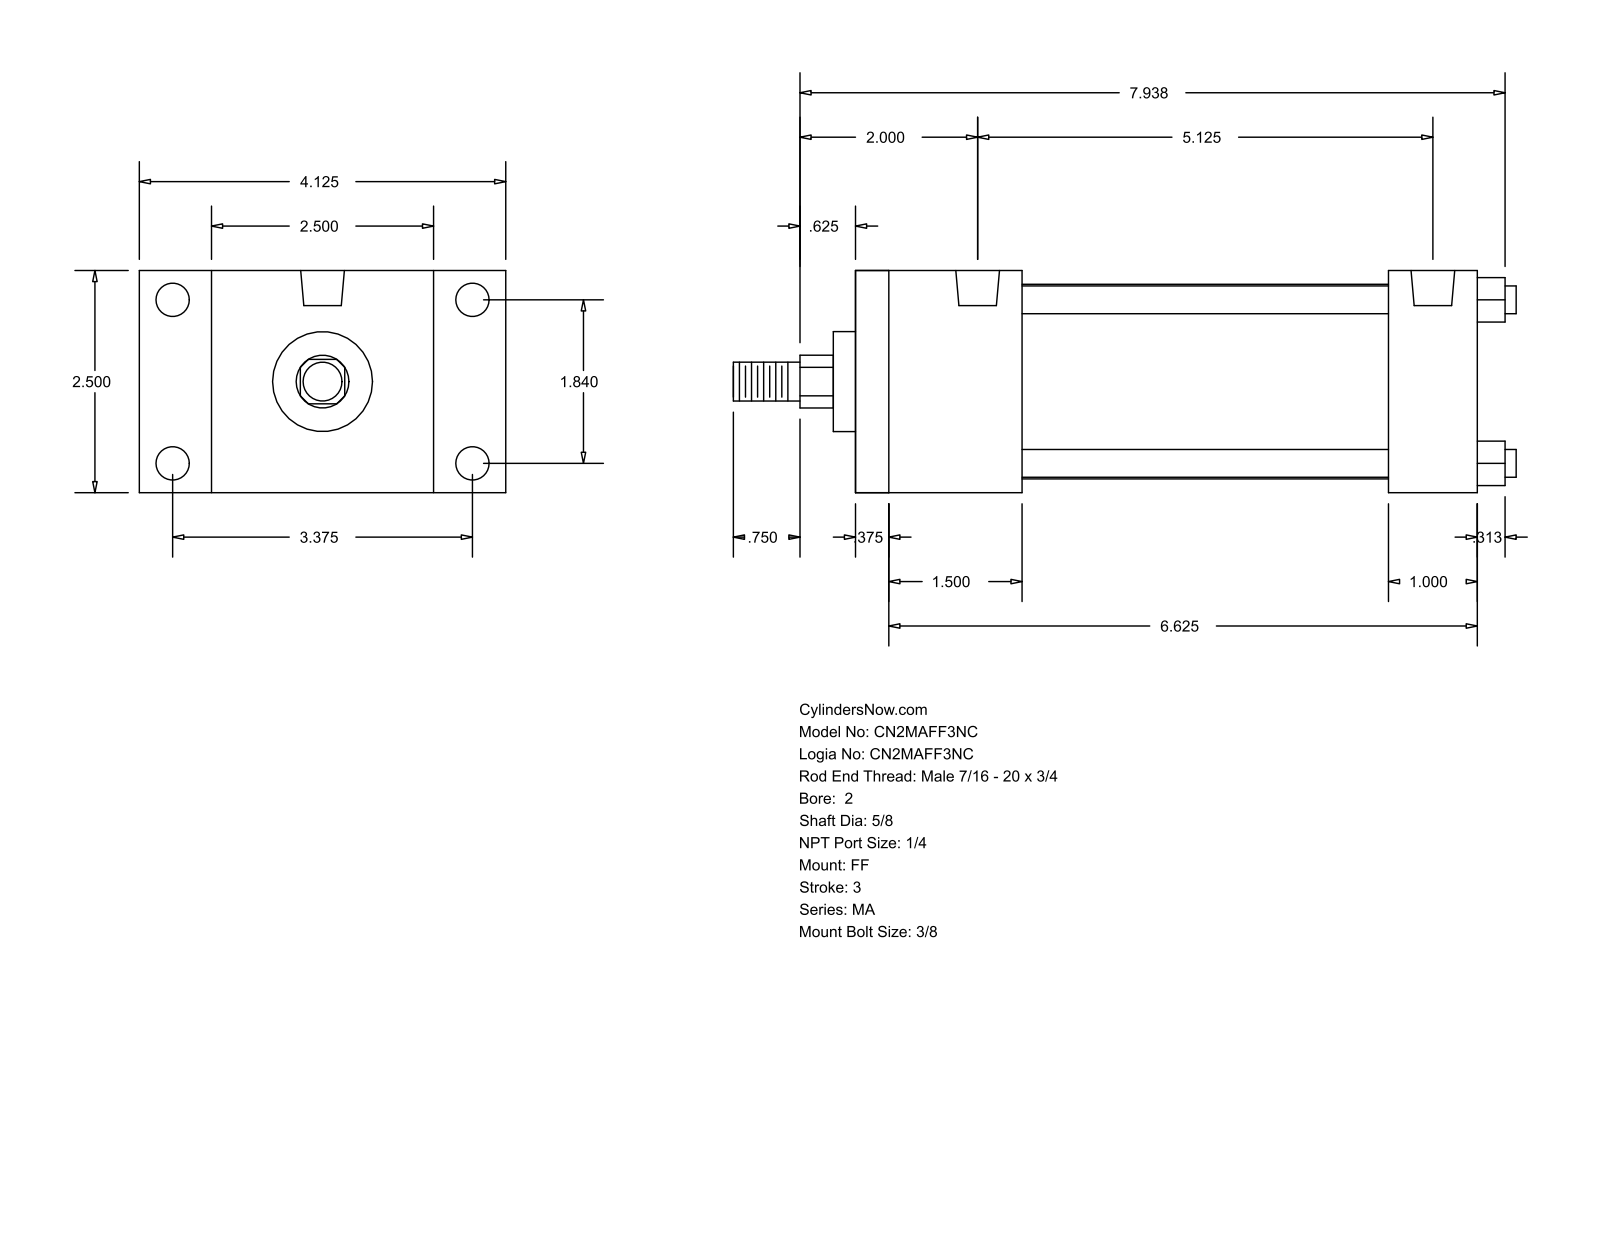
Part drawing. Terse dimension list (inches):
name: MA_FF__0200_0.625
written by: GSSL Pune (CONFIG_CONTROL_DESIGN)
unit: in
bodies: 0 solids, 92 faces (64 planar, 28 cylindrical, 0 other)
size: 8.813 × 4.125 × 2.5
holes: 4× ⌀0.313, 4× ⌀0.375, 2× ⌀0.492
bosses: 4× ⌀0.313, 1× ⌀2.19, 1× ⌀1.125, 1× ⌀0.625, 1× ⌀0.437
rounds: 1× R0.297
face distances: 2.5, 7, 6.625, 0.375, 4.125, 1, 1.5, 1.875, 6, 5.625
hole spacings: 1.84, 3.375, 3.844, 5.125
